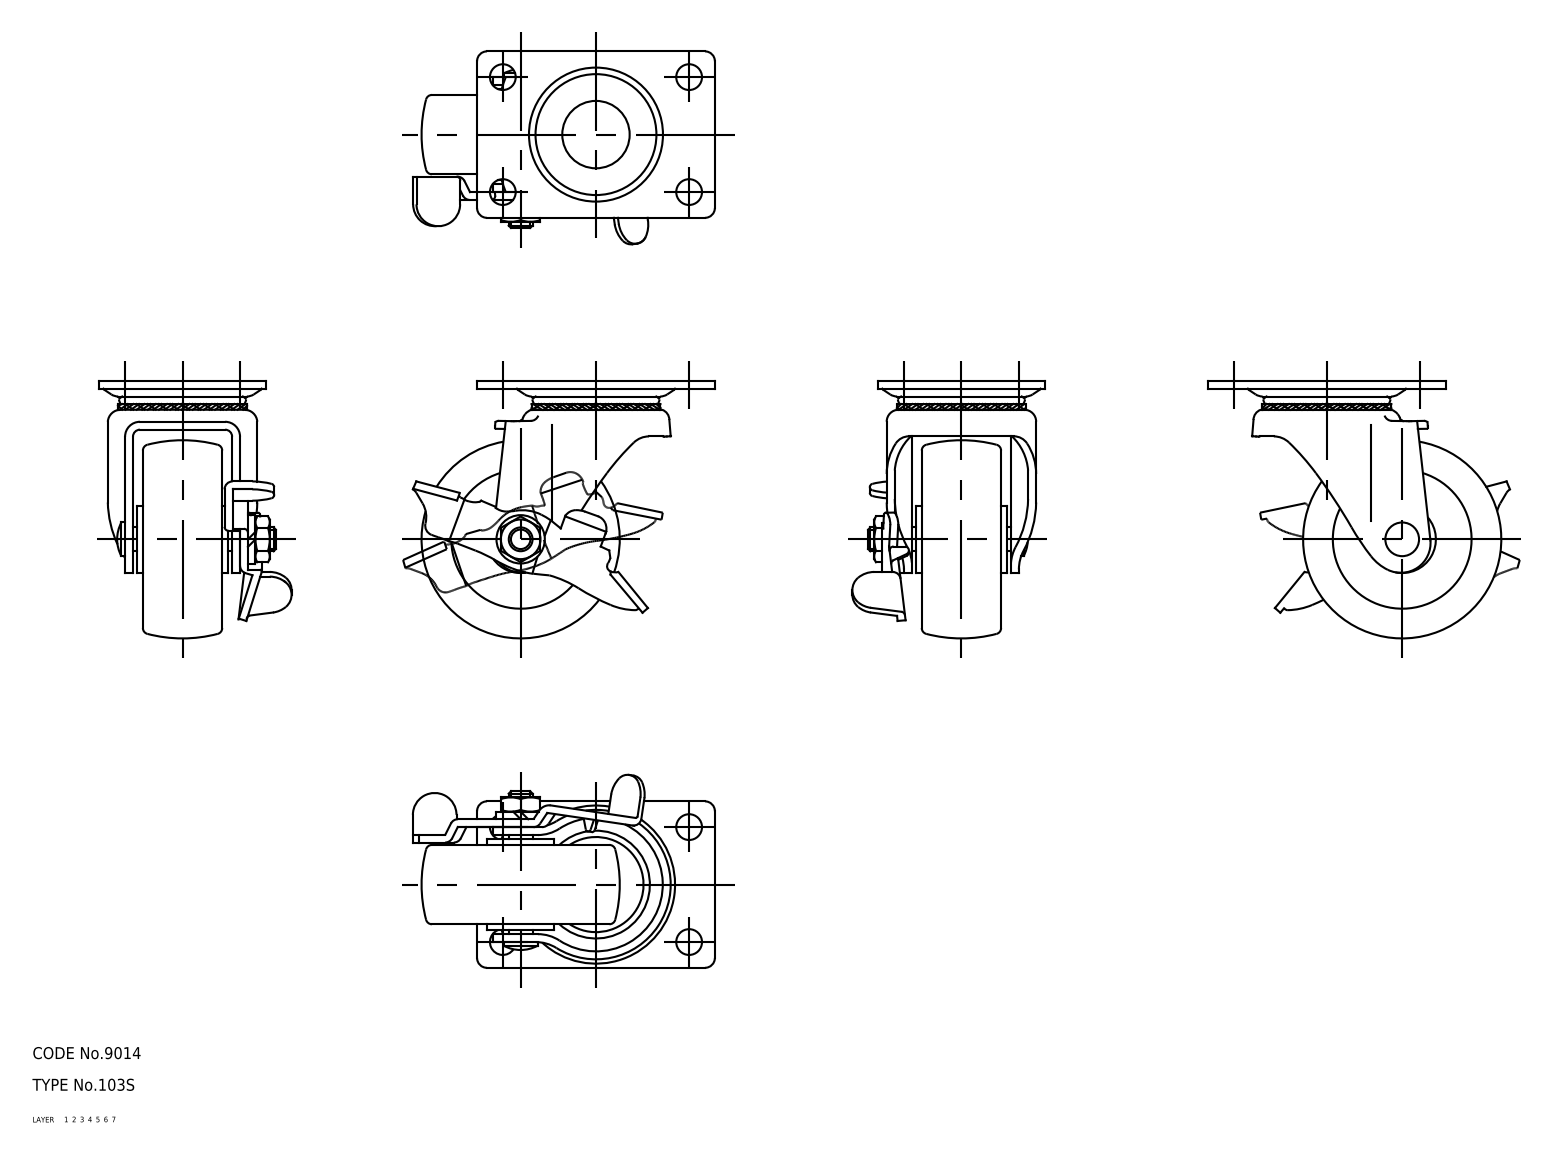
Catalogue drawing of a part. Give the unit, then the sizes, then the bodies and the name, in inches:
Units: inches
Overall size (bounding box): 3 × 2.559 × 1.911
Volume: 3.396 in³ · Surface area: 38.72 in²
Bodies: 5 solids, 314 faces (0 planar, 0 cylindrical, 314 other)
Part name (STEP PRODUCT): 67129545; 67129558; 67129571; 67129584 (+8 more)
STEP written by: CADfix (AUTOMOTIVE_DESIGN)
